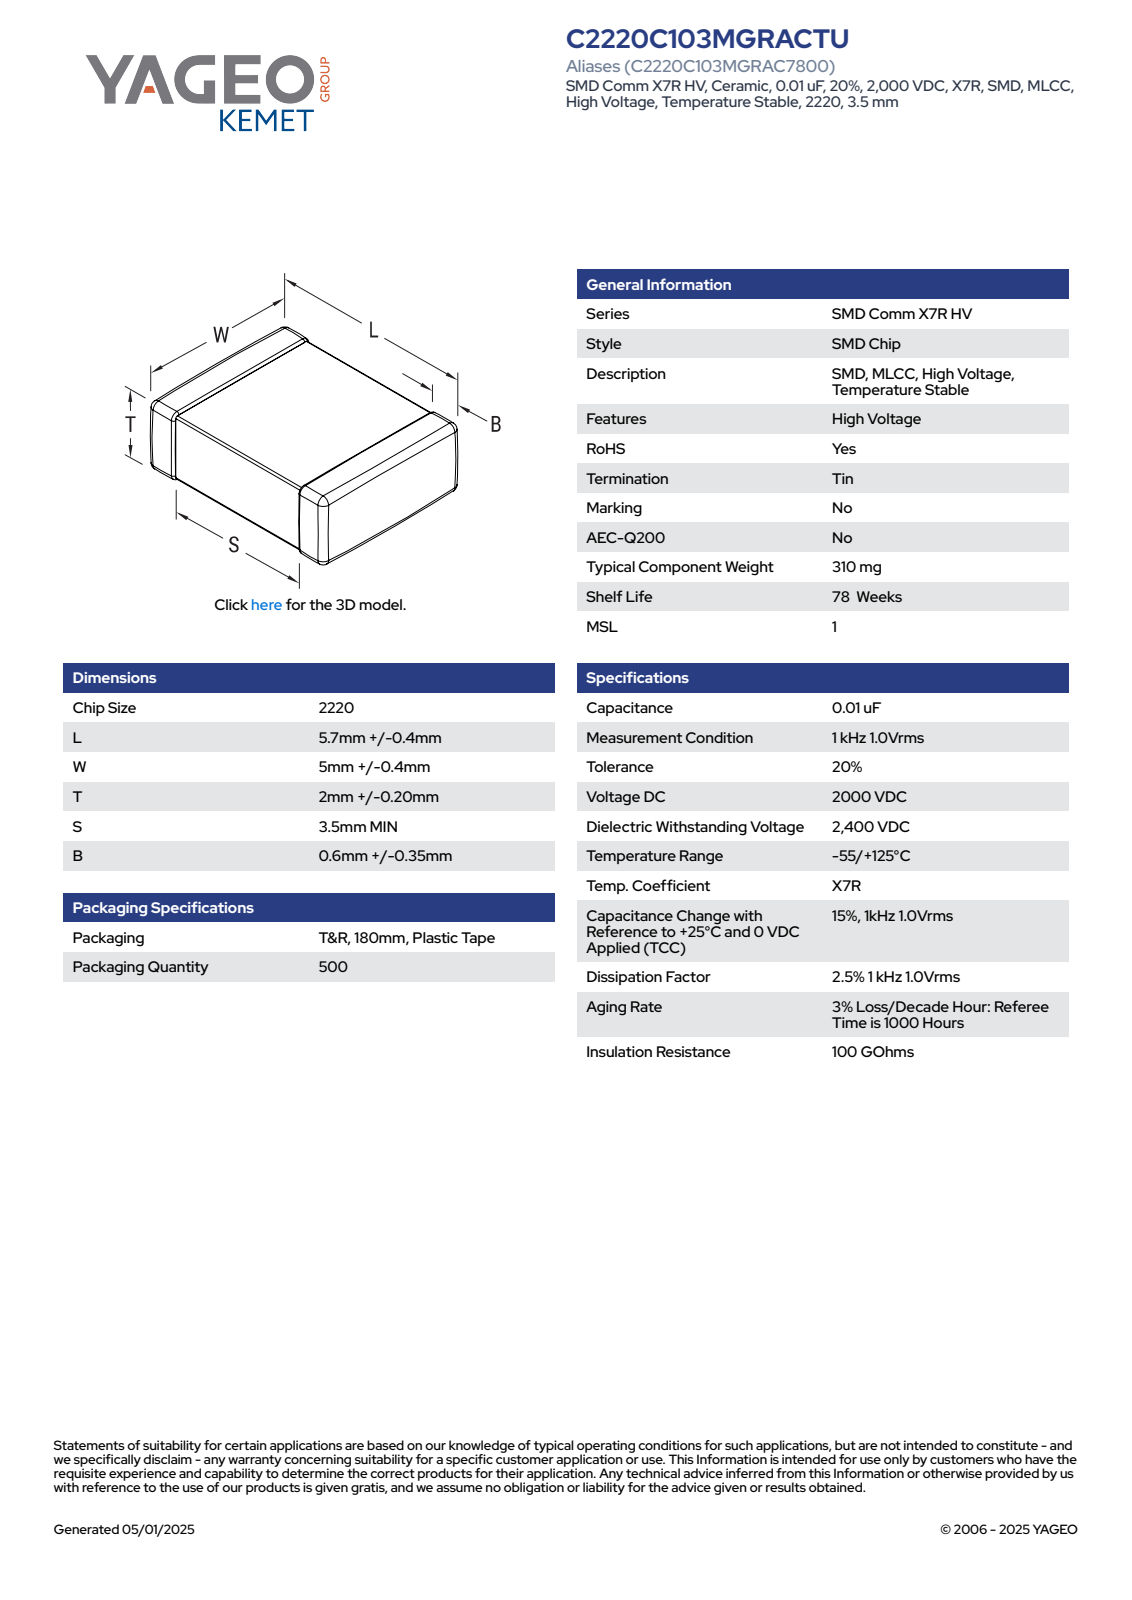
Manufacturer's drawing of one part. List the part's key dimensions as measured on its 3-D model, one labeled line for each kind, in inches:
Part name (STEP PRODUCT): CCS_CCSTD_2220_L6.1W5.4T2.2B0.6
STEP written by: SolidWorks 2021 (AUTOMOTIVE_DESIGN)
Units: inches
Bodies: 4 solids, 125 faces (71 planar, 38 cylindrical, 16 other)
Overall size (bounding box): 0.24 × 0.213 × 0.087
Volume: 0.004 in³ · Surface area: 0.18 in²
Partial cylindrical surfaces — rounded edges, fillets, slot ends (radius × count): R0.004 ×24
Main face-to-face distances: 0.078, 0.082, 0.24, 0.204, 0.087, 0.208, 0.213, 0.098, 0.142, 0.13
